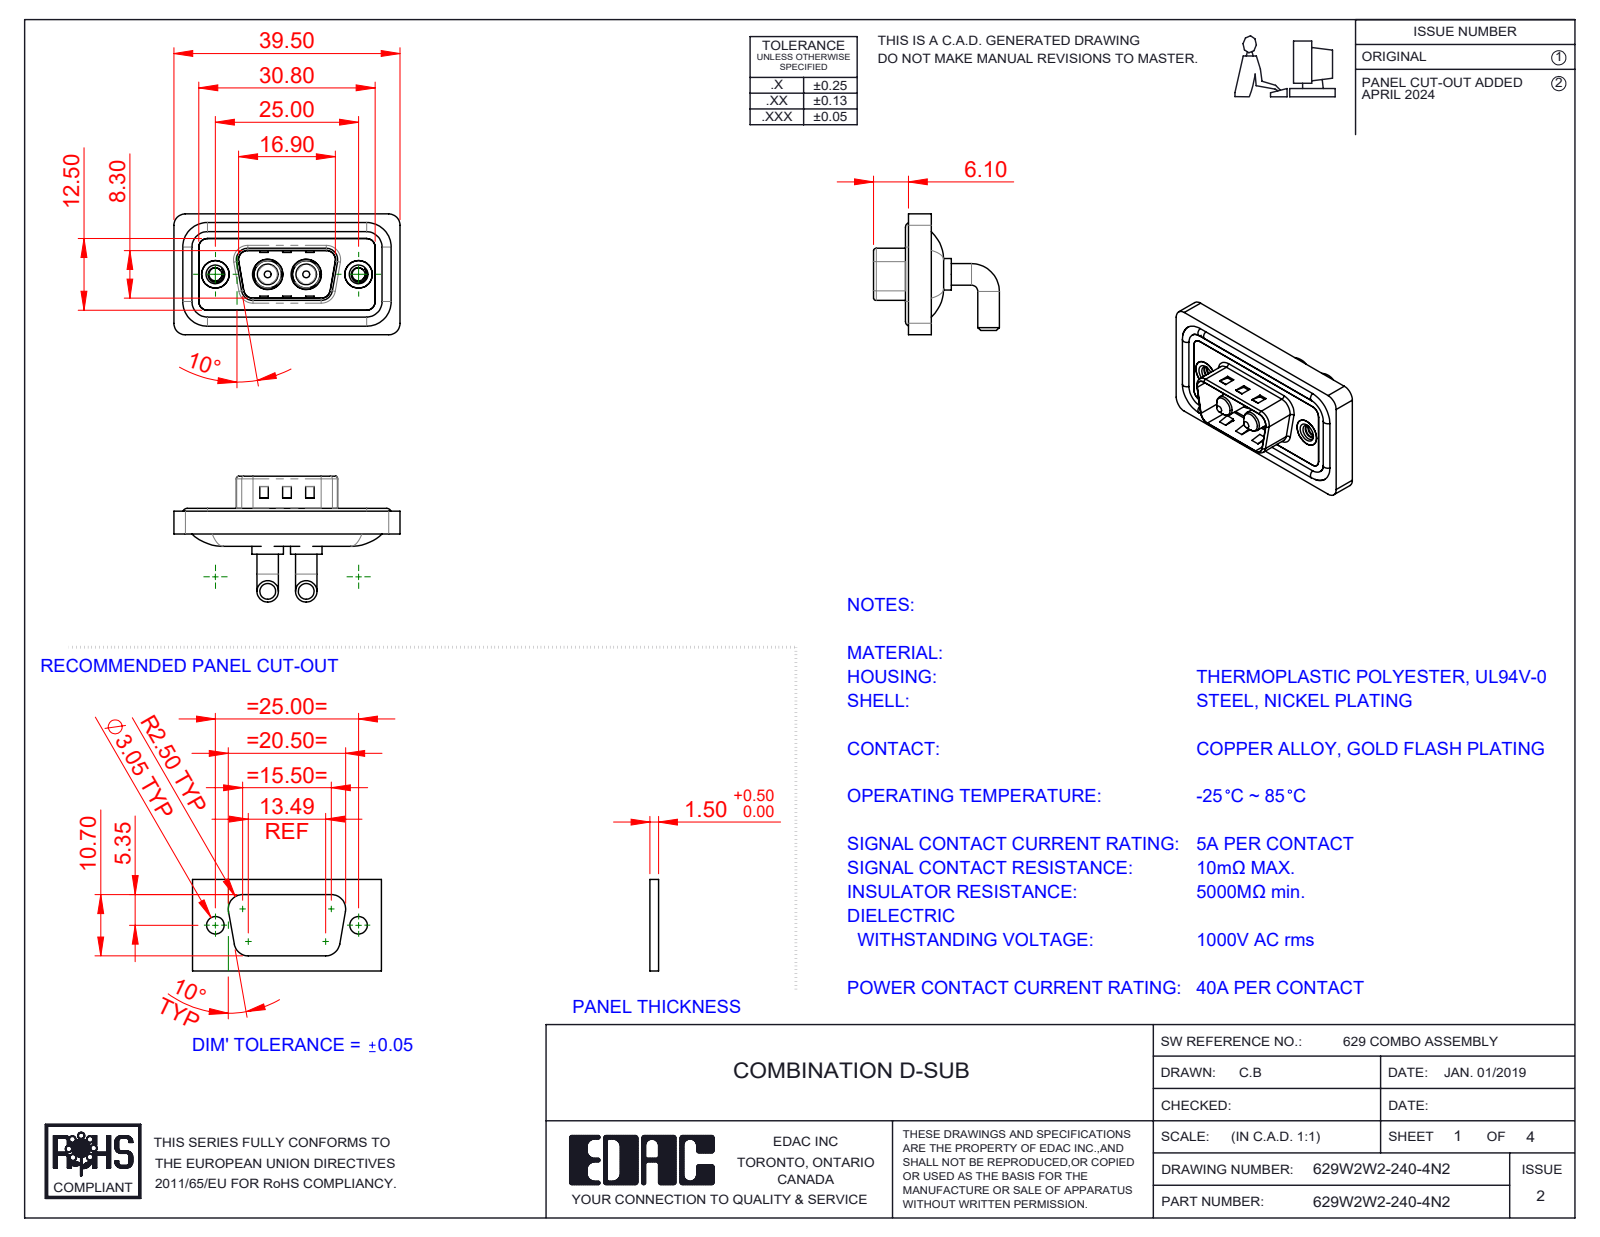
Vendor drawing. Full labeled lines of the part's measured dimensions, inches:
Part name (STEP PRODUCT): 629Combo Threaded Rivet_2; Power Pin_40A RA; 629Combo Housing_2W2; 629Combo Waterproof Housing_09 Contacts (+3 more)
STEP written by: SolidWorks 2023 (CONFIG_CONTROL_DESIGN)
Units: inches
Bodies: 11 solids, 497 faces (165 planar, 222 cylindrical, 110 other)
Overall size (bounding box): 1.555 × 0.865 × 0.831
Volume: 0.289 in³ · Surface area: 11.25 in²
Round holes (diameter × count): ⌀0.089 ×2, ⌀0.157 ×2, ⌀0.189 ×2, ⌀0.191 ×2, ⌀0.197 ×2, ⌀0.209 ×2
Round bosses / shafts (diameter × count): ⌀0.148 ×4, ⌀0.063 ×4, ⌀0.217 ×2, ⌀0.205 ×2, ⌀0.193 ×2, ⌀0.187 ×2, ⌀0.142 ×2
Partial cylindrical surfaces — rounded edges, fillets, slot ends (radius × count): R0.059 ×18, R0.079 ×18, R0.02 ×8, R0.063 ×8, R0.01 ×4, R0.024 ×4, R0.026 ×4, R0.035 ×4
Main face-to-face distances: 0.016, 0.114, 0.043, 0.031, 0.083, 0.098, 0.122, 0.063, 0.177, 0.059
Hole centre spacings: 0.36, 0.624, 0.265, 0.984
